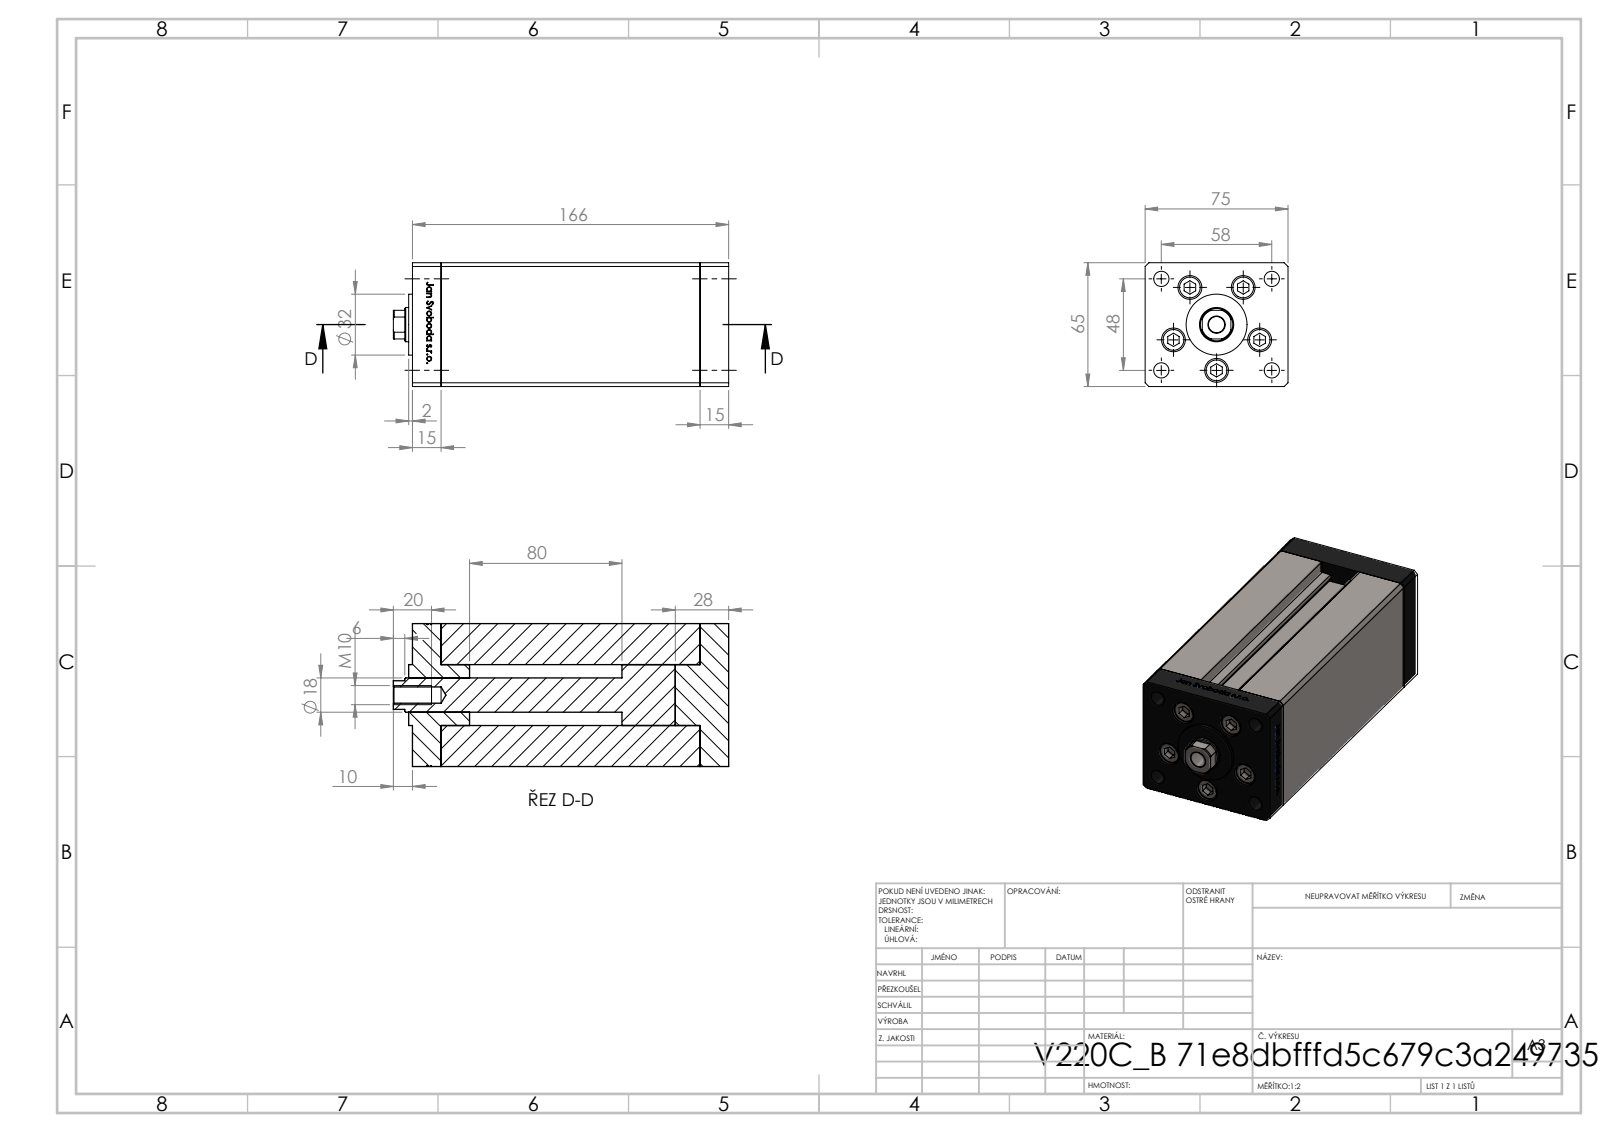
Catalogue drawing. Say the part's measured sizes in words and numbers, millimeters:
The part is named "V220C_B MIDDLE; V220C_VC_B; ALLEN BOLT; V220C BACK_B (+1 more)". Its 3-D file was written by "SolidWorks 2019 (CONFIG_CONTROL_DESIGN)". It is 14 solids with 1183 faces: 462 planar, 147 cylindrical and 574 other. Overall it measures 176 by 75 by 65 millimeters. Its volume is 722 498 cubic millimeters and its surface area 127 363 square millimeters. Round holes: 5 of diameter 9, 5 of diameter 12.5, 4 of diameter 8, 2 of diameter 2, 2 of diameter 13.16, 1 of diameter 8.5, 1 of diameter 18. Round bosses or shafts: 5 of diameter 8, 1 of diameter 32. Partial cylindrical surfaces (rounded edges, fillets, slot ends): 2 of radius 0.93, 1 of radius 8.5. The main face-to-face distances are 75, 65, 15, 136, 151, 166, 28, 13, 54.5, 10.5. The hole center spacings are 24, 37.64, 15.67, 17.22, 27.71, 28.83, 29, 32.63.
